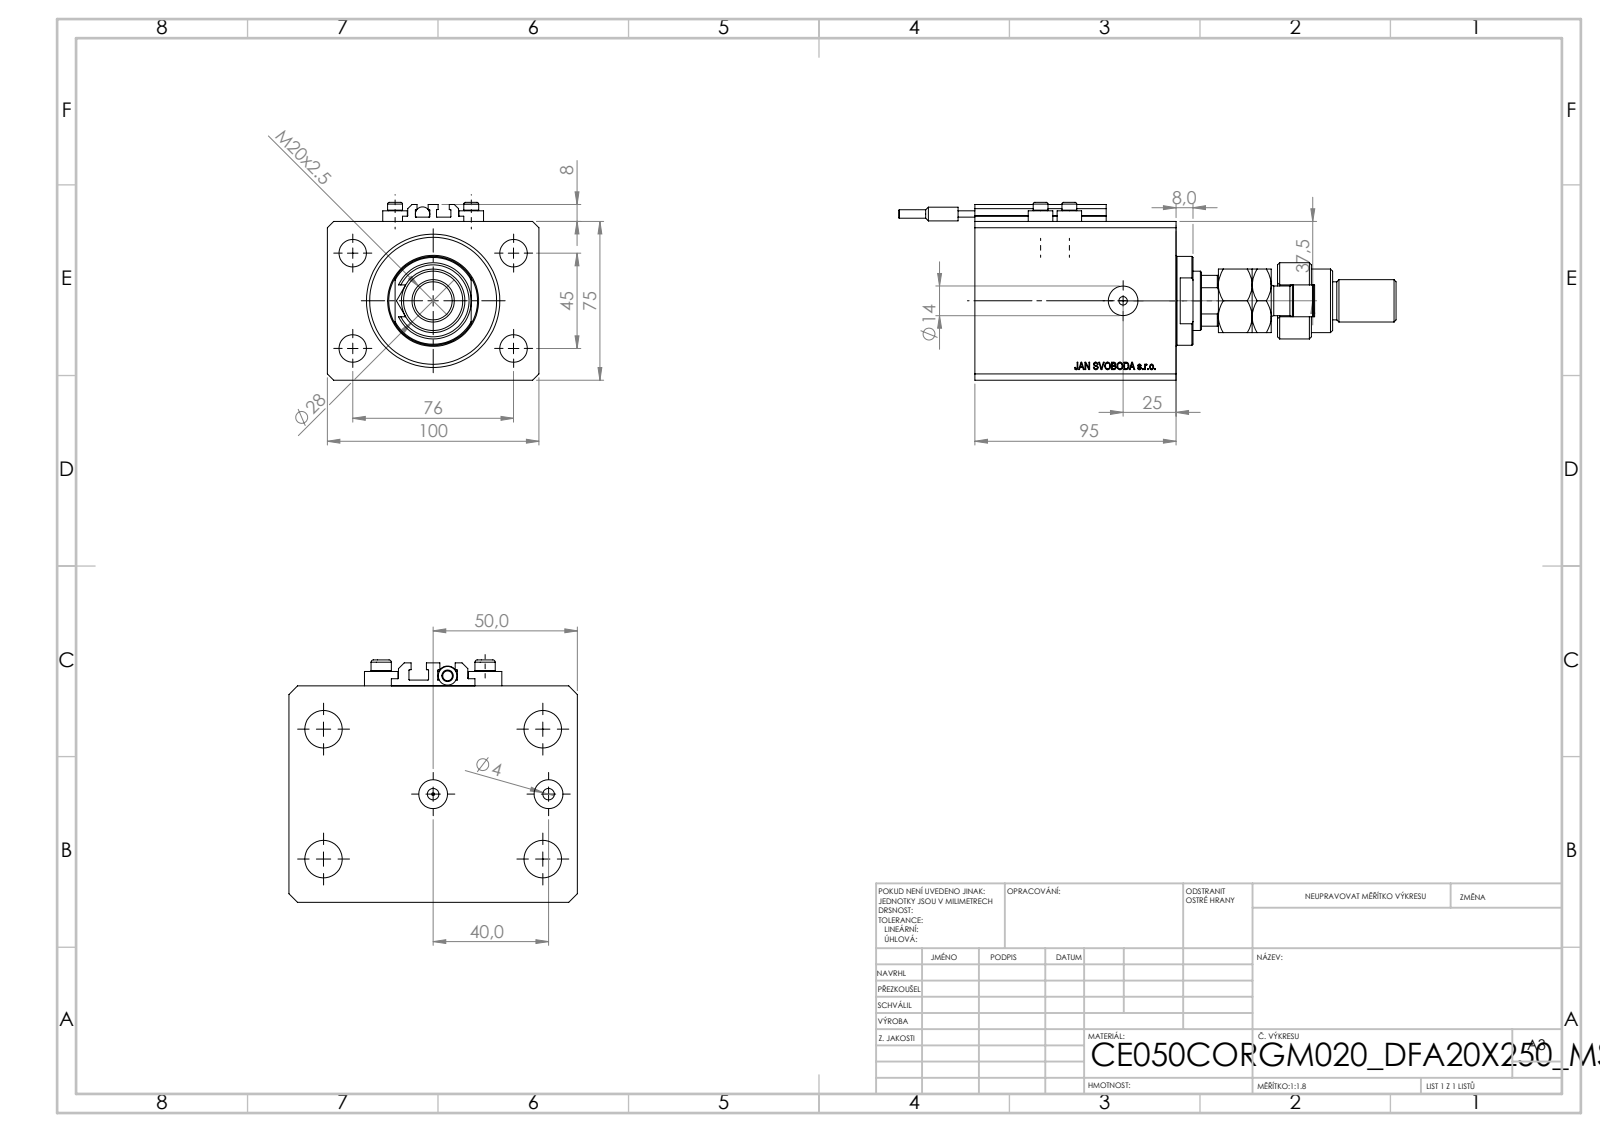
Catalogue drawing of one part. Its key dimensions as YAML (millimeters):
part_name: "MFA; V250CE_C_Body; FEMALE_PART_FOR_DFA; V250CE_VC_C (+3 more)"
step_written_by: "SolidWorks 2019 (CONFIG_CONTROL_DESIGN)"
units: millimeters
bodies: {solids: 11, faces: 1149, planar: 548, cylindrical: 107, other: 494}
overall_size: [235, 100, 84]
volume: 698342
surface_area: 132094
round_holes:
  - {diameter: 4, count: 8}
  - {diameter: 13, count: 4}
  - {diameter: 10, count: 2}
  - {diameter: 14, count: 2}
  - {diameter: 1.25, count: 1}
  - {diameter: 18.5, count: 1}
  - {diameter: 28, count: 1}
  - {diameter: 50, count: 1}
  - {diameter: 63, count: 1}
round_bosses_or_shafts:
  - {diameter: 11.6, count: 4}
  - {diameter: 7, count: 4}
  - {diameter: 42, count: 1}
  - {diameter: 36, count: 1}
  - {diameter: 30, count: 1}
  - {diameter: 22, count: 1}
  - {diameter: 20, count: 1}
  - {diameter: 18, count: 1}
partial_cylinders:
  - {radius: 0.2, count: 10}
  - {radius: 7.5, count: 1}
  - {radius: 12, count: 1}
  - {radius: 13.5, count: 1}
face_to_face_distances: [75, 100, 20, 95, 11.9, 83.1, 63.1, 40, 30, 3]
hole_center_spacings: [44.16, 45, 13.6, 22.59, 36, 38.48, 76, 81.18]
